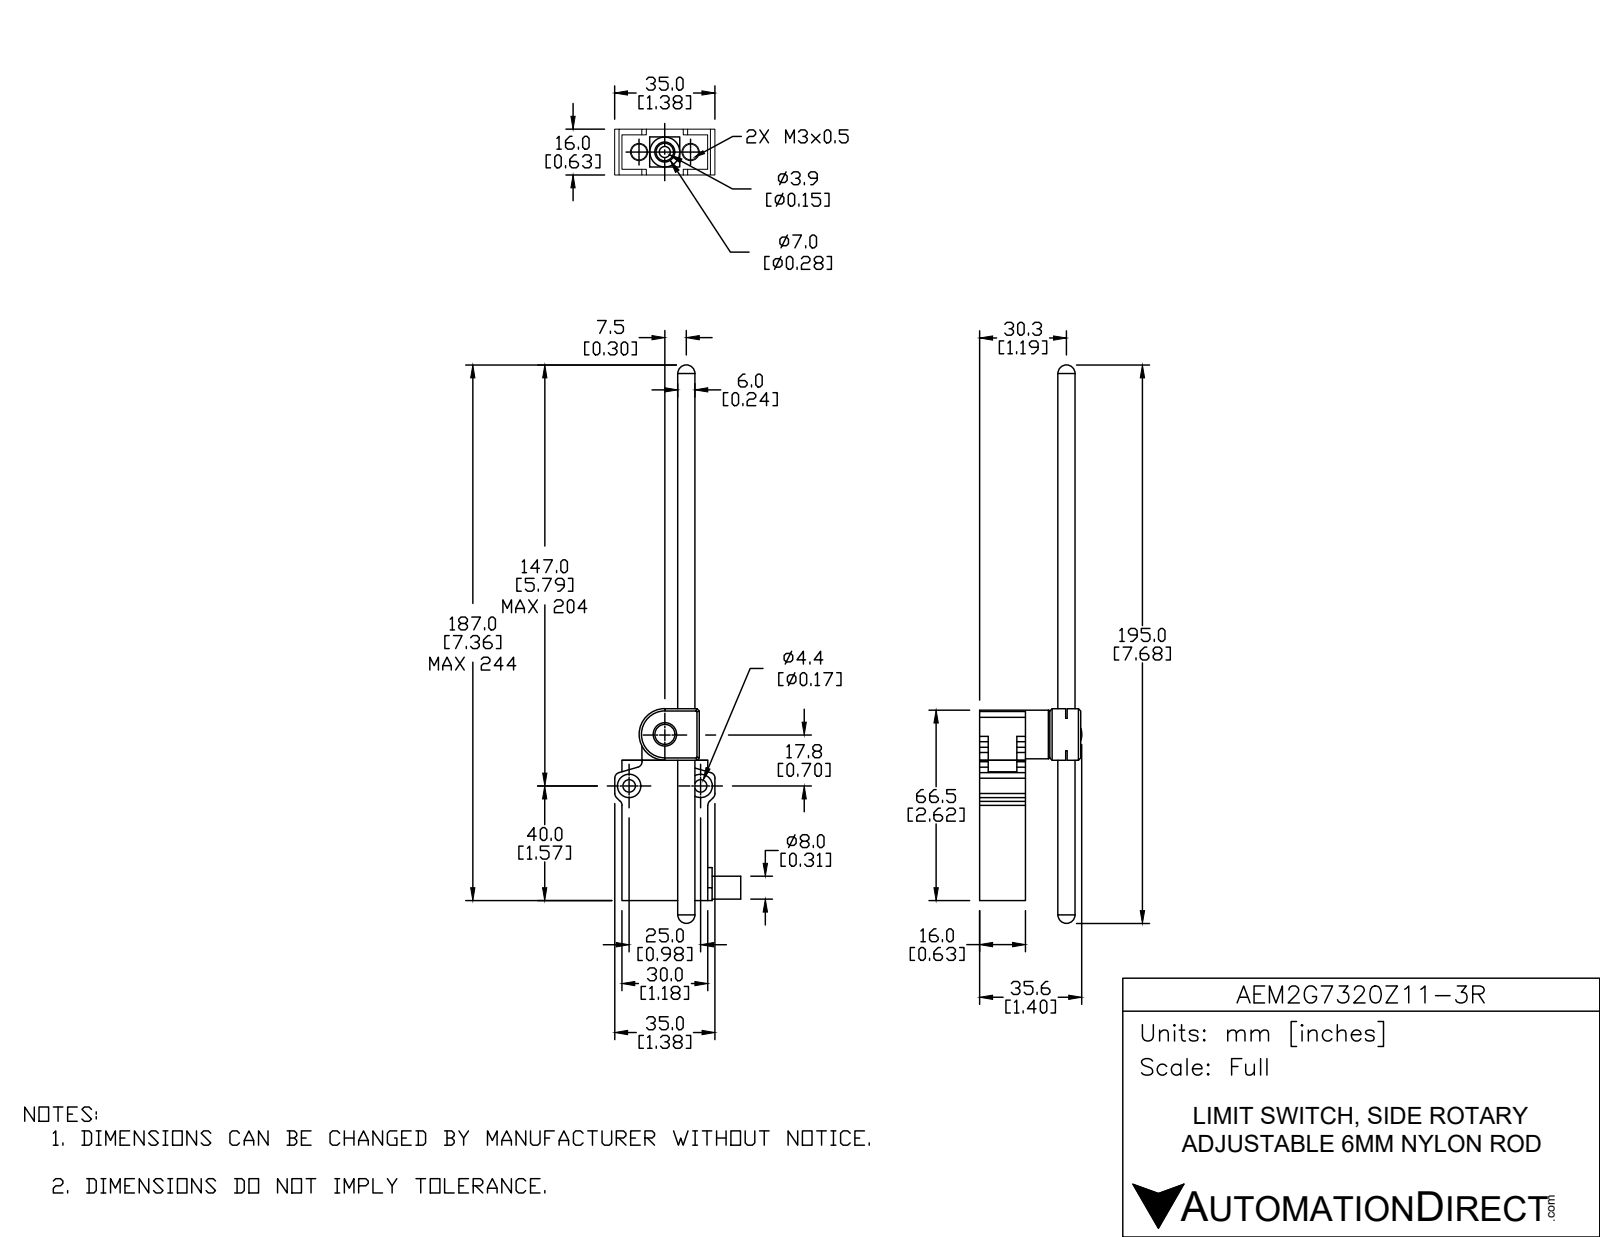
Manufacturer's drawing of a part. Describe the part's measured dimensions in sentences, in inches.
The part is named "AEM2G7320Z11-3R". Its 3-D file was written by "SolidWorks 2017 (AUTOMOTIVE_DESIGN)". It is 7 solids with 169 faces: 95 planar, 57 cylindrical and 17 other. Overall it measures 7.84 by 1.87 by 1.374 inches. Its volume is 2.217 cubic inches and its surface area 23.55 square inches. Round holes: 2 of diameter 0.118, 2 of diameter 0.173, 2 of diameter 0.323, 1 of diameter 0.138, 1 of diameter 0.197, 1 of diameter 0.236, 1 of diameter 0.315. Round bosses or shafts: 1 of diameter 0.622, 1 of diameter 0.323, 1 of diameter 0.276. Partial cylindrical surfaces (rounded edges, fillets, slot ends): 8 of radius 0.079, 1 of radius 0.256, 1 of radius 0.354. The main face-to-face distances are 0.63, 1.181, 0.177, 1.929, 0.354, 0.535, 1.165, 0.358, 0.28, 0.902. The hole center spacings are 0.863, 0.748, 0.857, 0.984, 1.065.
